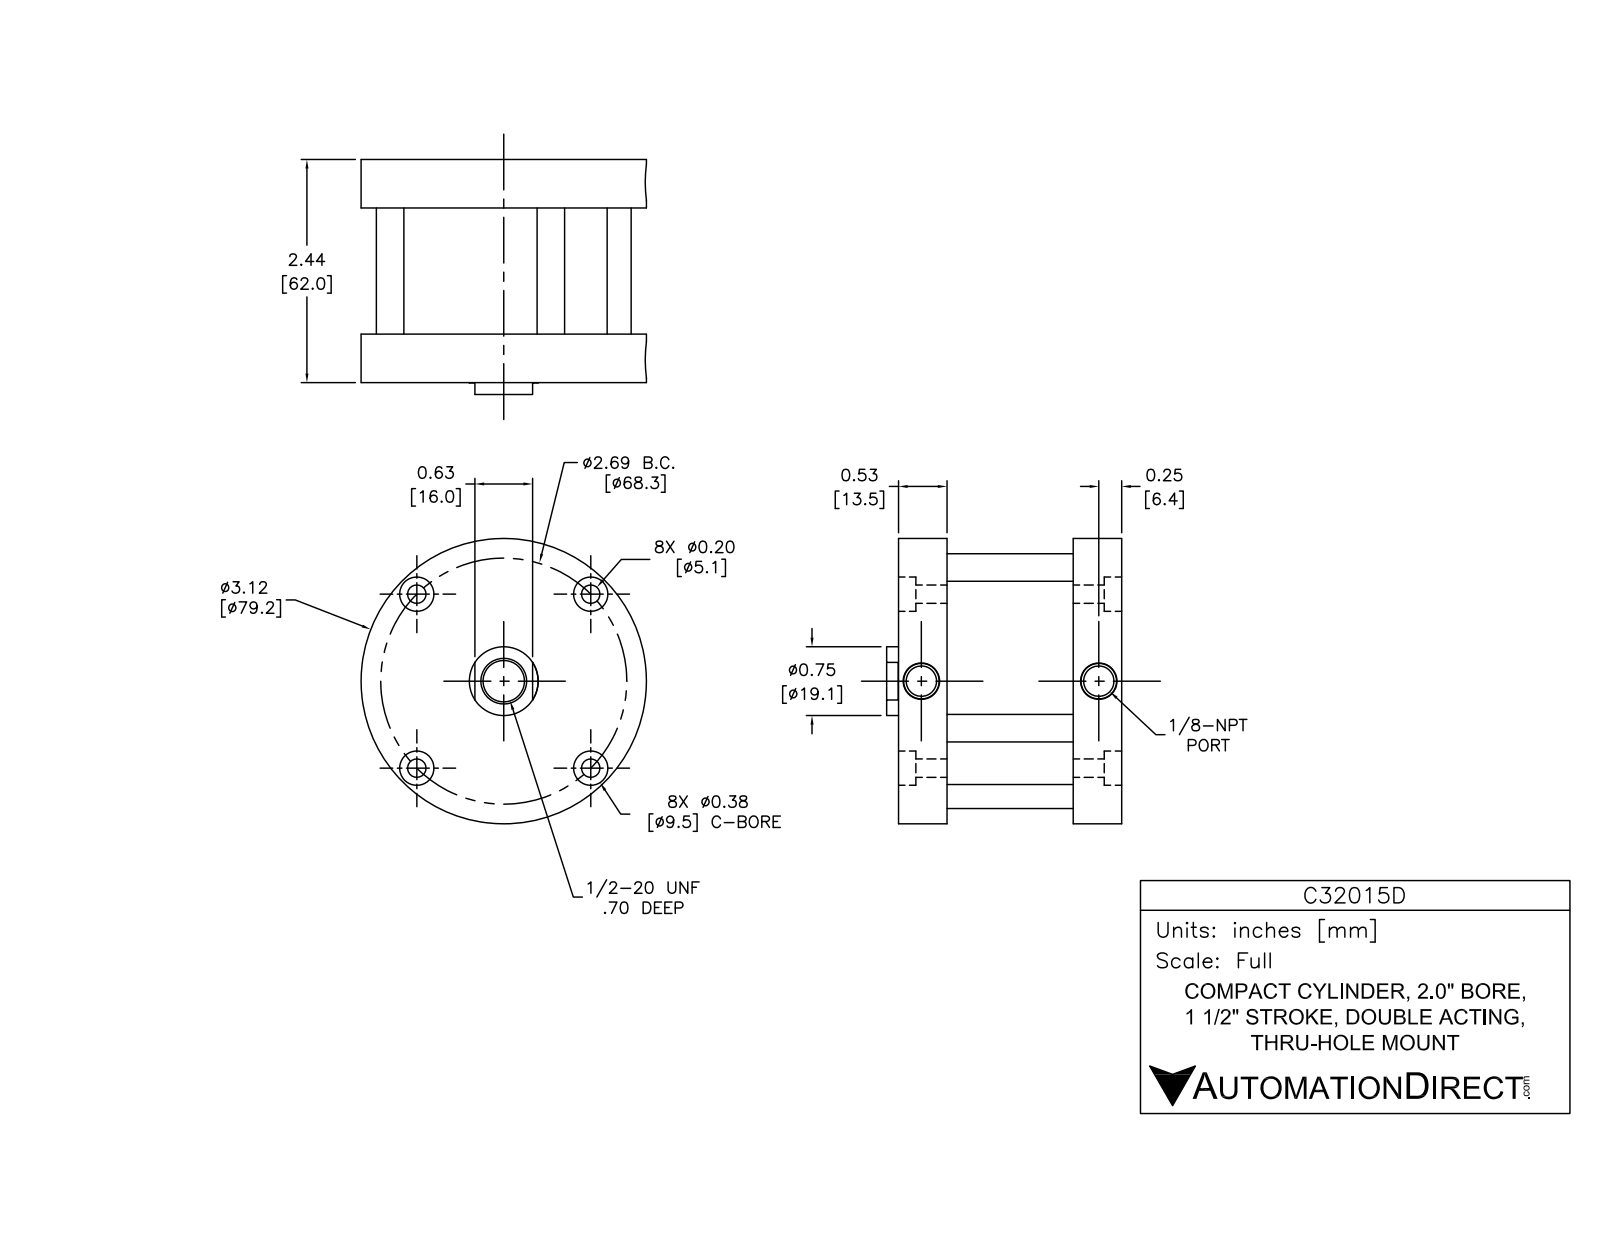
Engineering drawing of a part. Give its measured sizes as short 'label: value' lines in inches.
name: C32015D; C32015D-FO1_BM_r; C32015D-FO1_BM_rod; C32015D-FO1_BM_heads (2) (+3 more)
written by: SolidWorks 2014 (AUTOMOTIVE_DESIGN)
unit: in
bodies: 9 solids, 165 faces (49 planar, 98 cylindrical, 18 other)
size: 3.12 × 3.12 × 2.57
volume: 8.96 in³; area: 98.52 in²
holes: 4× ⌀0.2, 4× ⌀0.218, 4× ⌀0.343, 2× ⌀0.125, 1× ⌀0.446, 1× ⌀0.75, 1× ⌀0.752, 1× ⌀2, 1× ⌀2.06
bosses: 4× ⌀0.4, 1× ⌀3.12
face distances: 1.63, 0.25, 0.28, 2.44, 2.16, 1.91, 1.91, 0.53, 0.53, 1.38
hole spacings: 0.432, 1.345, 1.345, 1.572, 1.902, 1.902, 2.183, 2.655
